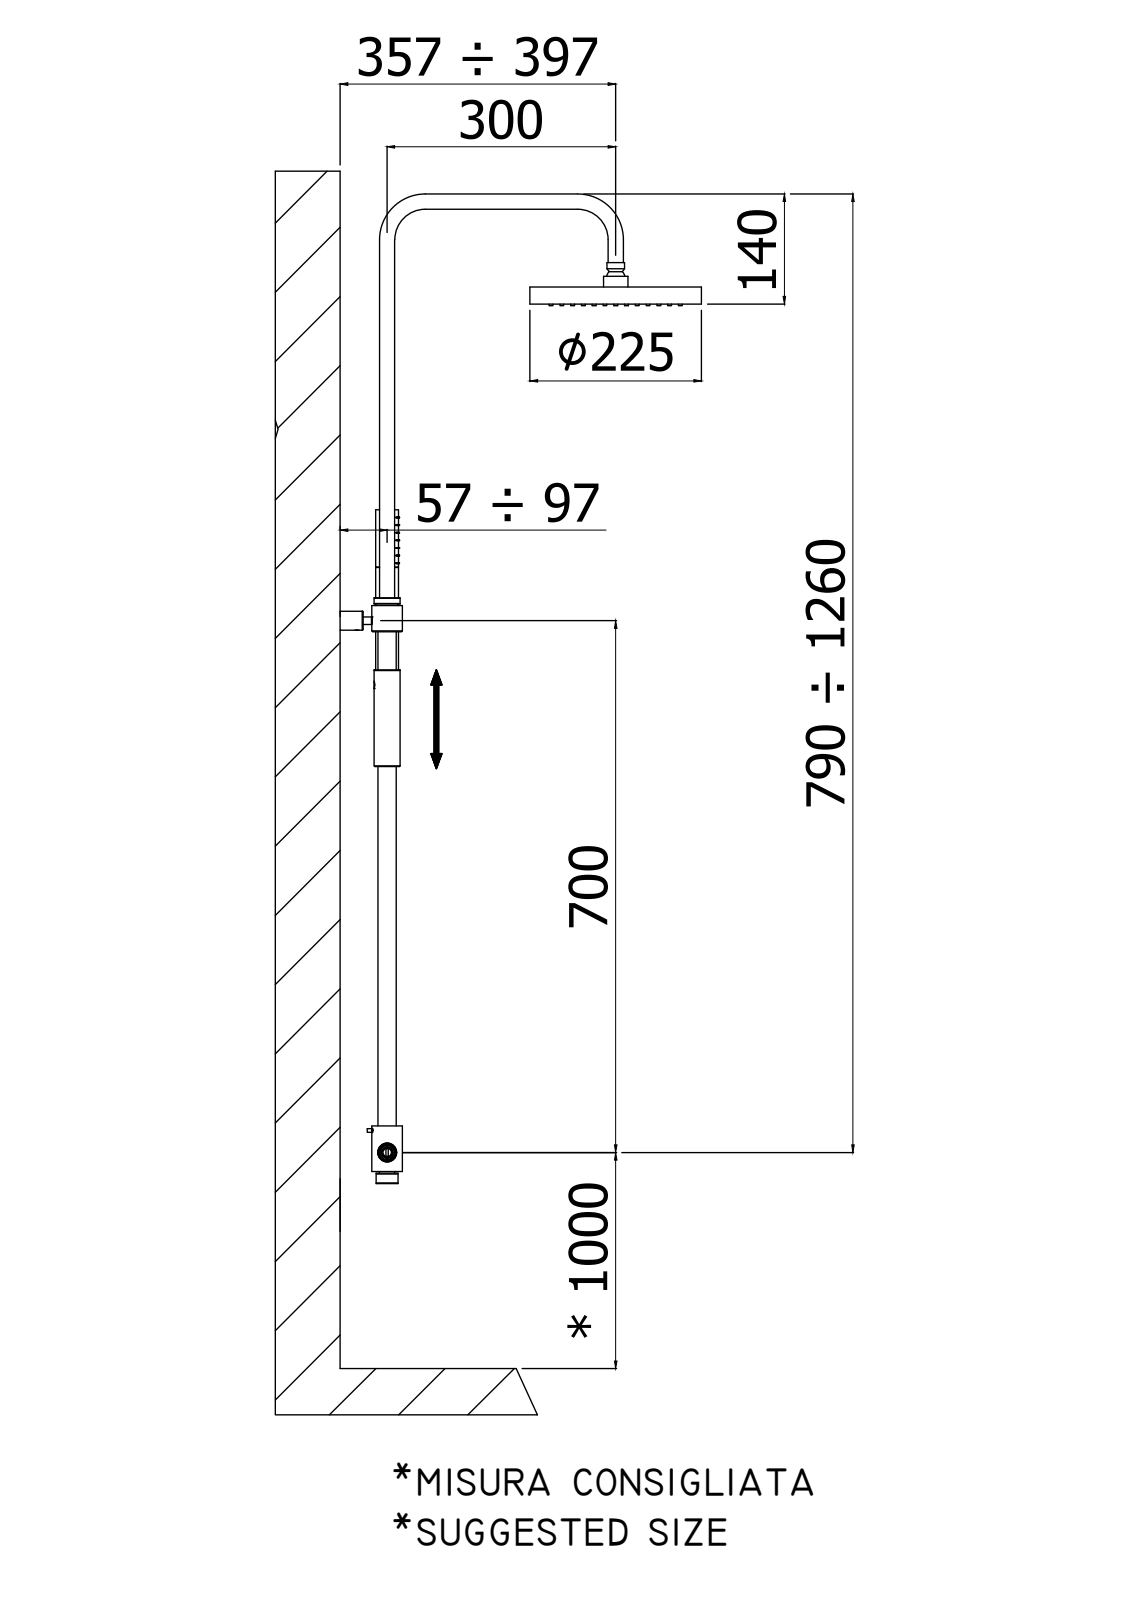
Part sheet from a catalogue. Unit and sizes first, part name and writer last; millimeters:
Units: millimetres
Overall size (bounding box): 1235 × 491.3 × 225
Round holes (diameter × count): ⌀1.2 ×80, ⌀1.5 ×45, ⌀5 ×4, ⌀17 ×4, ⌀3.3 ×2, ⌀3.5 ×2, ⌀10 ×2, ⌀10.5 ×2, ⌀12 ×2, ⌀25 ×2, ⌀27 ×2, ⌀4.2 ×1
Round bosses / shafts (diameter × count): ⌀20 ×4, ⌀21 ×3, ⌀225 ×1, ⌀40 ×1, ⌀37 ×1, ⌀34 ×1, ⌀32 ×1, ⌀29.8 ×1
Partial cylindrical surfaces — rounded edges, fillets, slot ends (radius × count): R0.3 ×24, R1 ×6, R7.8 ×2, R9.8 ×2, R10 ×2, R5.5 ×1, R6.5 ×1, R6.75 ×1
Main face-to-face distances: 6.5, 10, 1078.5, 1085, 555.75, 17.75, 198, 331, 60, 1018.5
Hole centre spacings: 7.91, 13.76, 20.01, 6.5, 28.16, 90, 13, 26.39
Volume: 681 658 mm³ · Surface area: 446 320 mm²
Bodies: 11 solids, 1408 faces (484 planar, 510 cylindrical, 414 other)
Part name (STEP PRODUCT): ZCOL611CR
STEP written by: CREO PARAMETRIC BY PTC INC, 2020044 (CONFIG_CONTROL_DESIGN)
